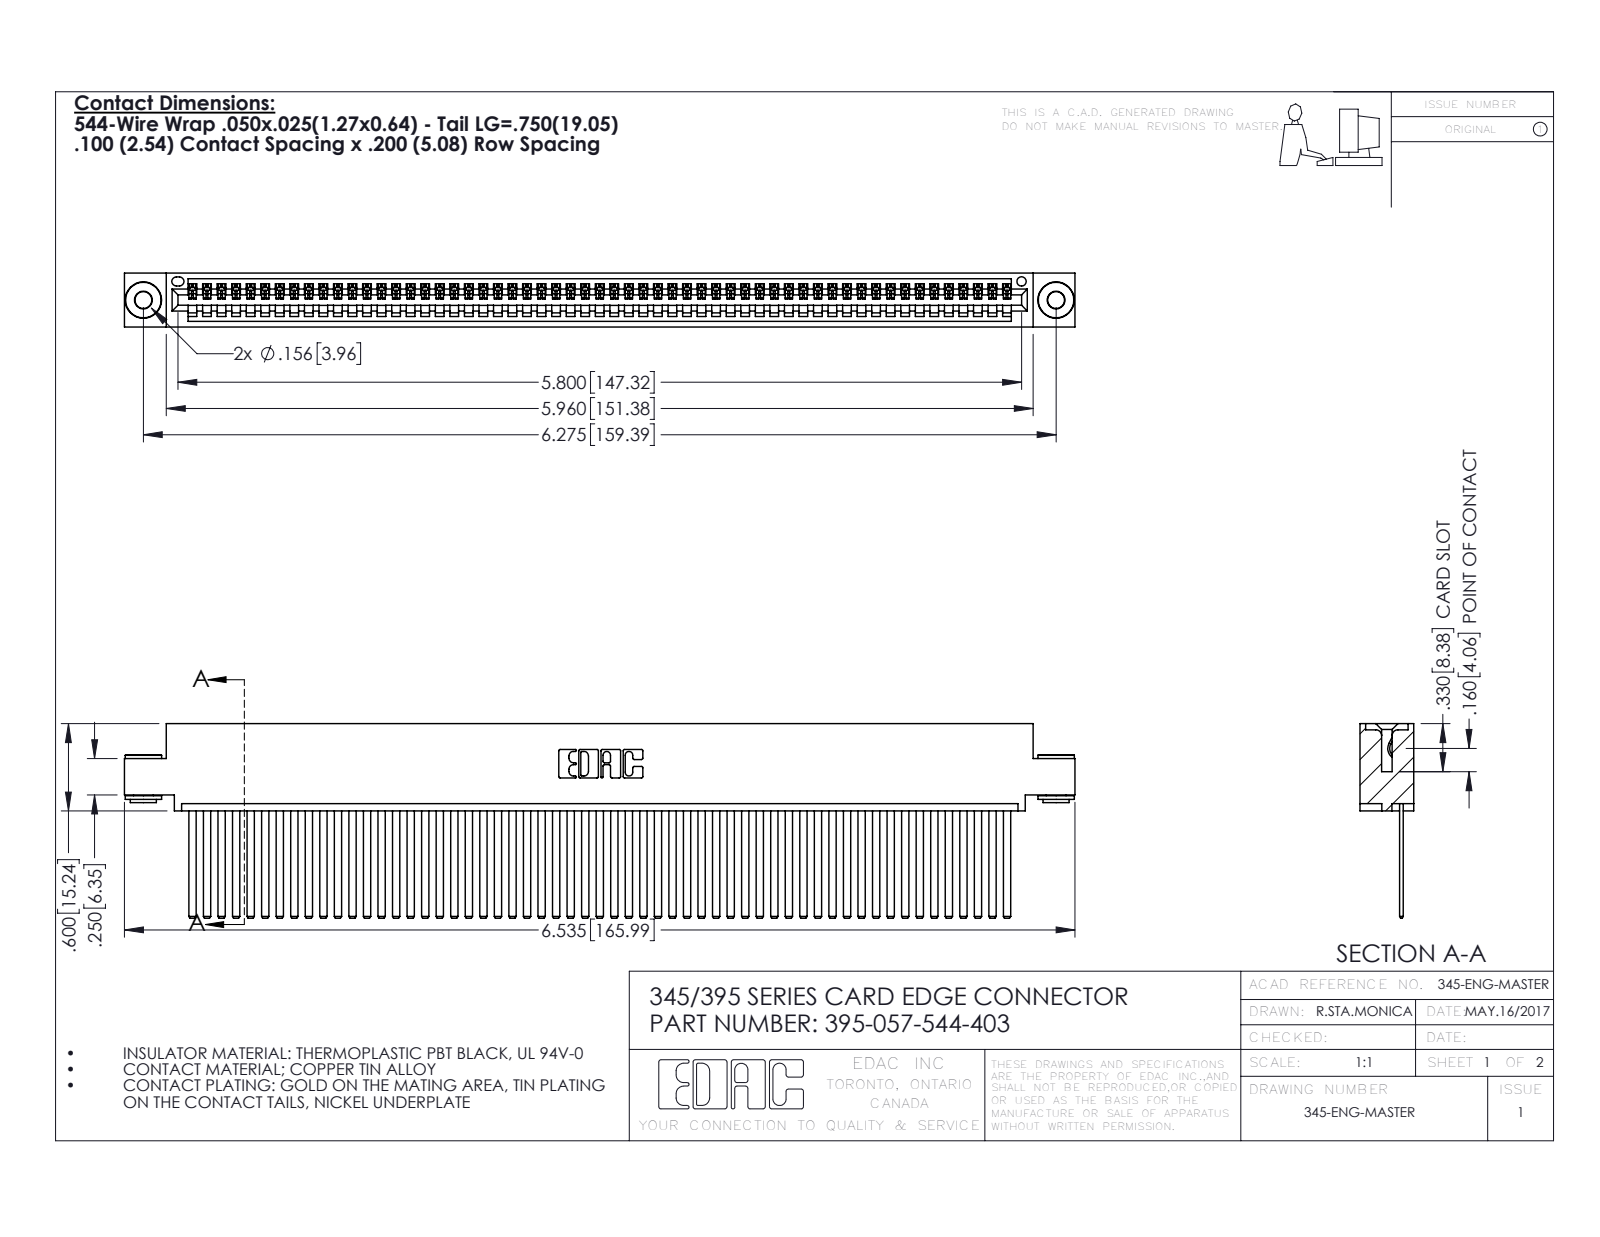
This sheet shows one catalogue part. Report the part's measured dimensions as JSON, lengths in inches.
{"part_name": "345-250-002_345-250-002-102; 345-292-001_345-293-144; 345 Part_0.110 Offset - 0.156 Dia-TH; 395-057-544-403", "step_written_by": "SolidWorks 2016 (CONFIG_CONTROL_DESIGN)", "units": "inches", "bodies": {"solids": 60, "faces": 3132, "planar": 2146, "cylindrical": 978, "other": 8}, "overall_size": [6.535, 1.337, 0.37], "volume_in3": 1.007, "surface_area_in2": 37.82, "round_holes": [[0.116, 2], [0.156, 2], [0.064, 1]], "round_bosses_or_shafts": [[0.25, 2], [0.18, 2], [0.136, 2]], "partial_cylinders_radius": [[0.006, 114], [0.01, 22], [0.007, 6], [0.031, 6], [0.026, 3], [0.031, 2], [0.04, 2], [0.014, 1]], "face_to_face_distances": [0.072, 0.298, 0.025, 0.098, 0.272, 0.37, 0.2, 0.225, 0.149, 0.072], "hole_center_spacings": [0.27, 6.039, 6.275]}
